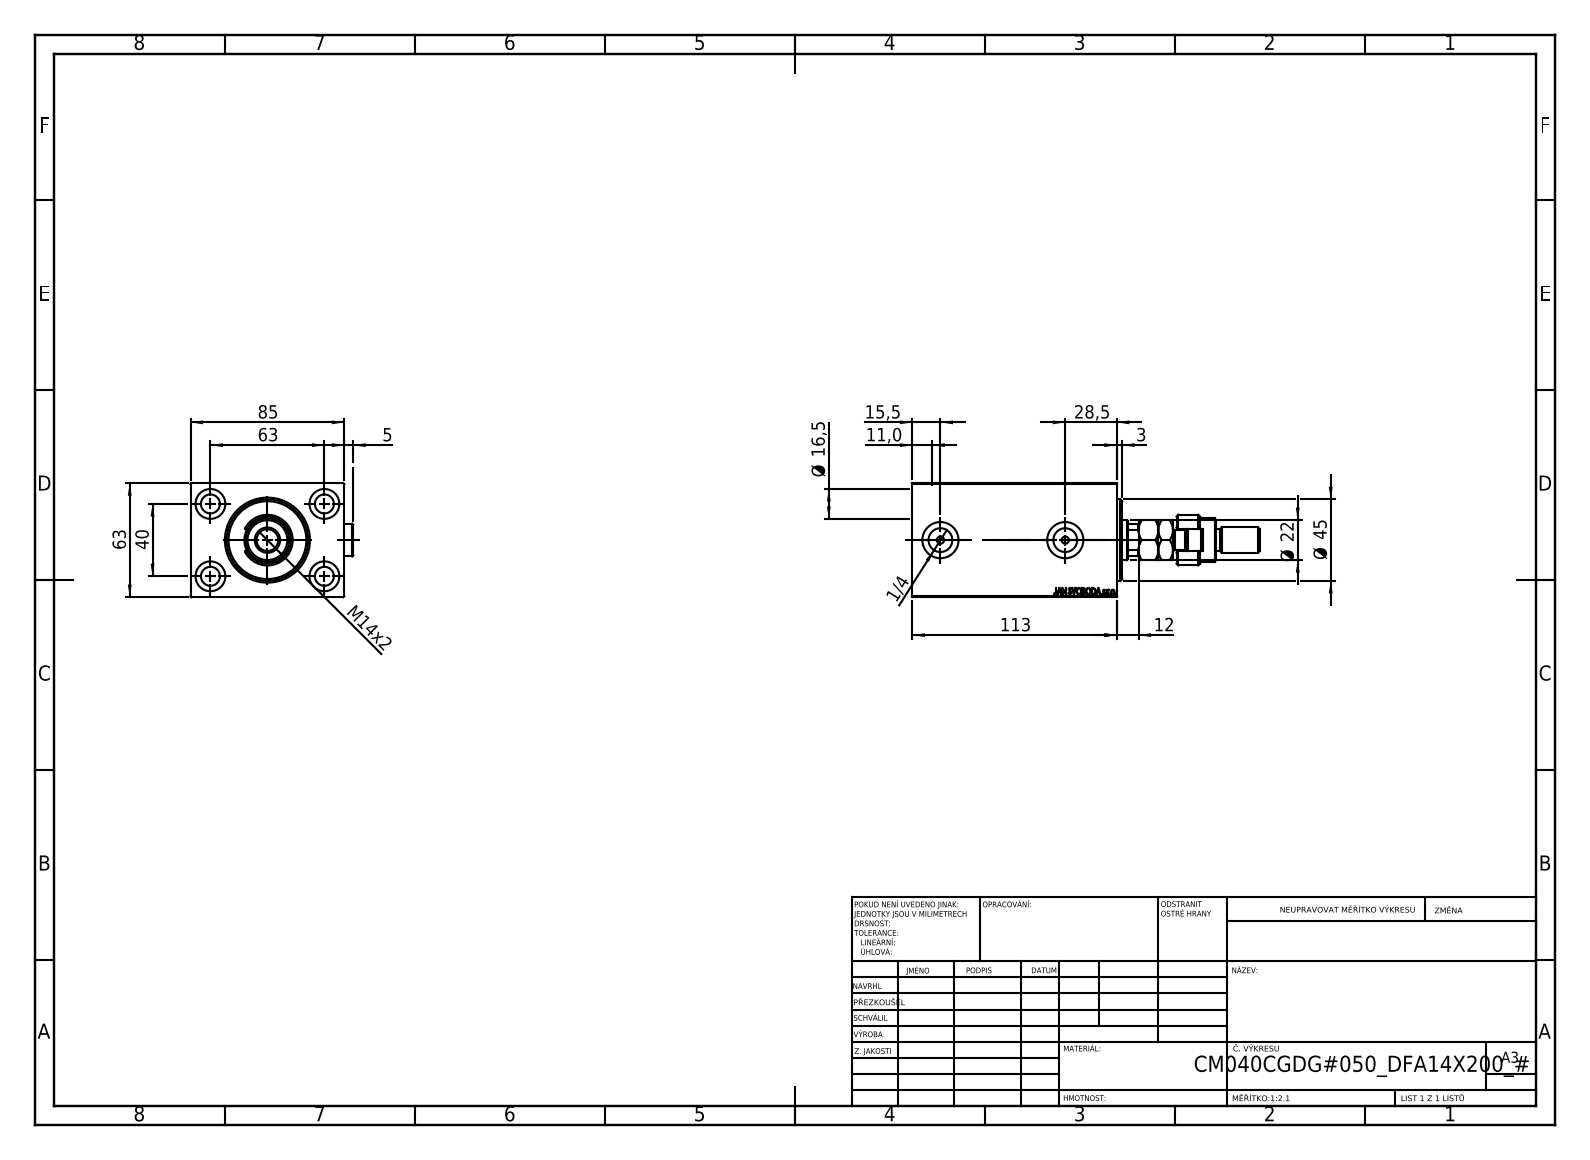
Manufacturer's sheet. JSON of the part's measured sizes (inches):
{"part_name": "Zatka_OIL_PORT; MFA; V450CM_C_VCP; V450CM_VC_B (+2 more)", "step_written_by": "SolidWorks 2019 (CONFIG_CONTROL_DESIGN)", "units": "inches", "bodies": {"solids": 7, "faces": 1001, "planar": 470, "cylindrical": 89, "other": 442}, "overall_size": [7.559, 3.539, 2.48], "volume_in3": 32.49, "surface_area_in2": 160.6, "round_holes": [[0.413, 4], [0.65, 4], [0.157, 2], [0.518, 2], [0.787, 2], [0.492, 1], [0.866, 1], [1.004, 1], [1.575, 1], [1.654, 1], [1.772, 1]], "round_bosses_or_shafts": [[0.709, 3], [1.102, 1], [0.945, 1], [0.551, 1], [0.472, 1], [0.433, 1]], "partial_cylinders_radius": [[0.384, 1], [0.413, 1]], "face_to_face_distances": [2.48, 3.346, 0.472, 3.976, 4.449, 2.008, 3.343, 0.118, 0.591, 3.504], "hole_center_spacings": [1.469, 1.575, 2.48, 2.938, 2.717]}
